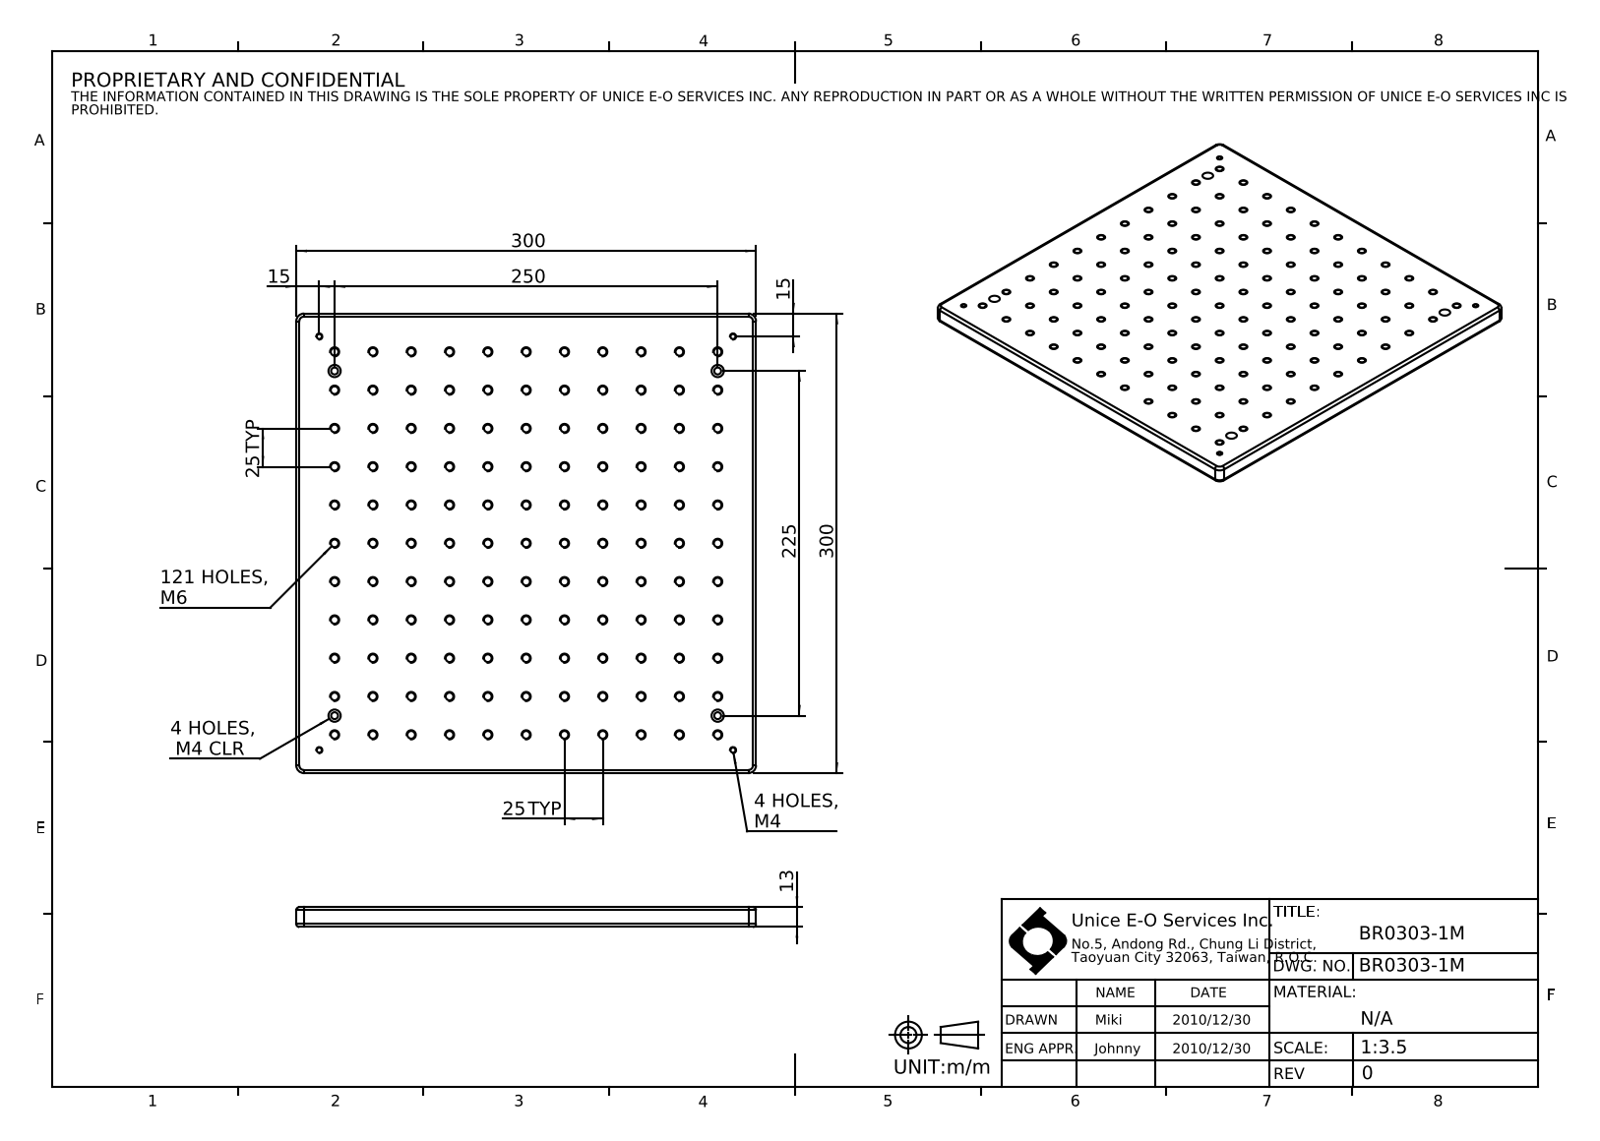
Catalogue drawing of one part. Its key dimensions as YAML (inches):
part_name: "BR0303-1M"
step_written_by: "SolidWorks 2016 (CONFIG_CONTROL_DESIGN)"
units: inches
bodies: {solids: 1, faces: 296, planar: 10, cylindrical: 278, other: 8}
overall_size: [11.811, 11.811, 0.512]
volume: 69.26
surface_area: 332.8
round_holes:
  - {diameter: 0.197, count: 121}
  - {diameter: 0.13, count: 4}
  - {diameter: 0.177, count: 4}
  - {diameter: 0.315, count: 4}
partial_cylinders:
  - {radius: 0.079, count: 8}
  - {radius: 0.197, count: 4}
face_to_face_distances: [0.512, 11.811, 0.276, 0.236]
hole_center_spacings: [0.984, 1.392, 1.969, 2.201, 2.953, 3.113, 3.937, 4.058]
